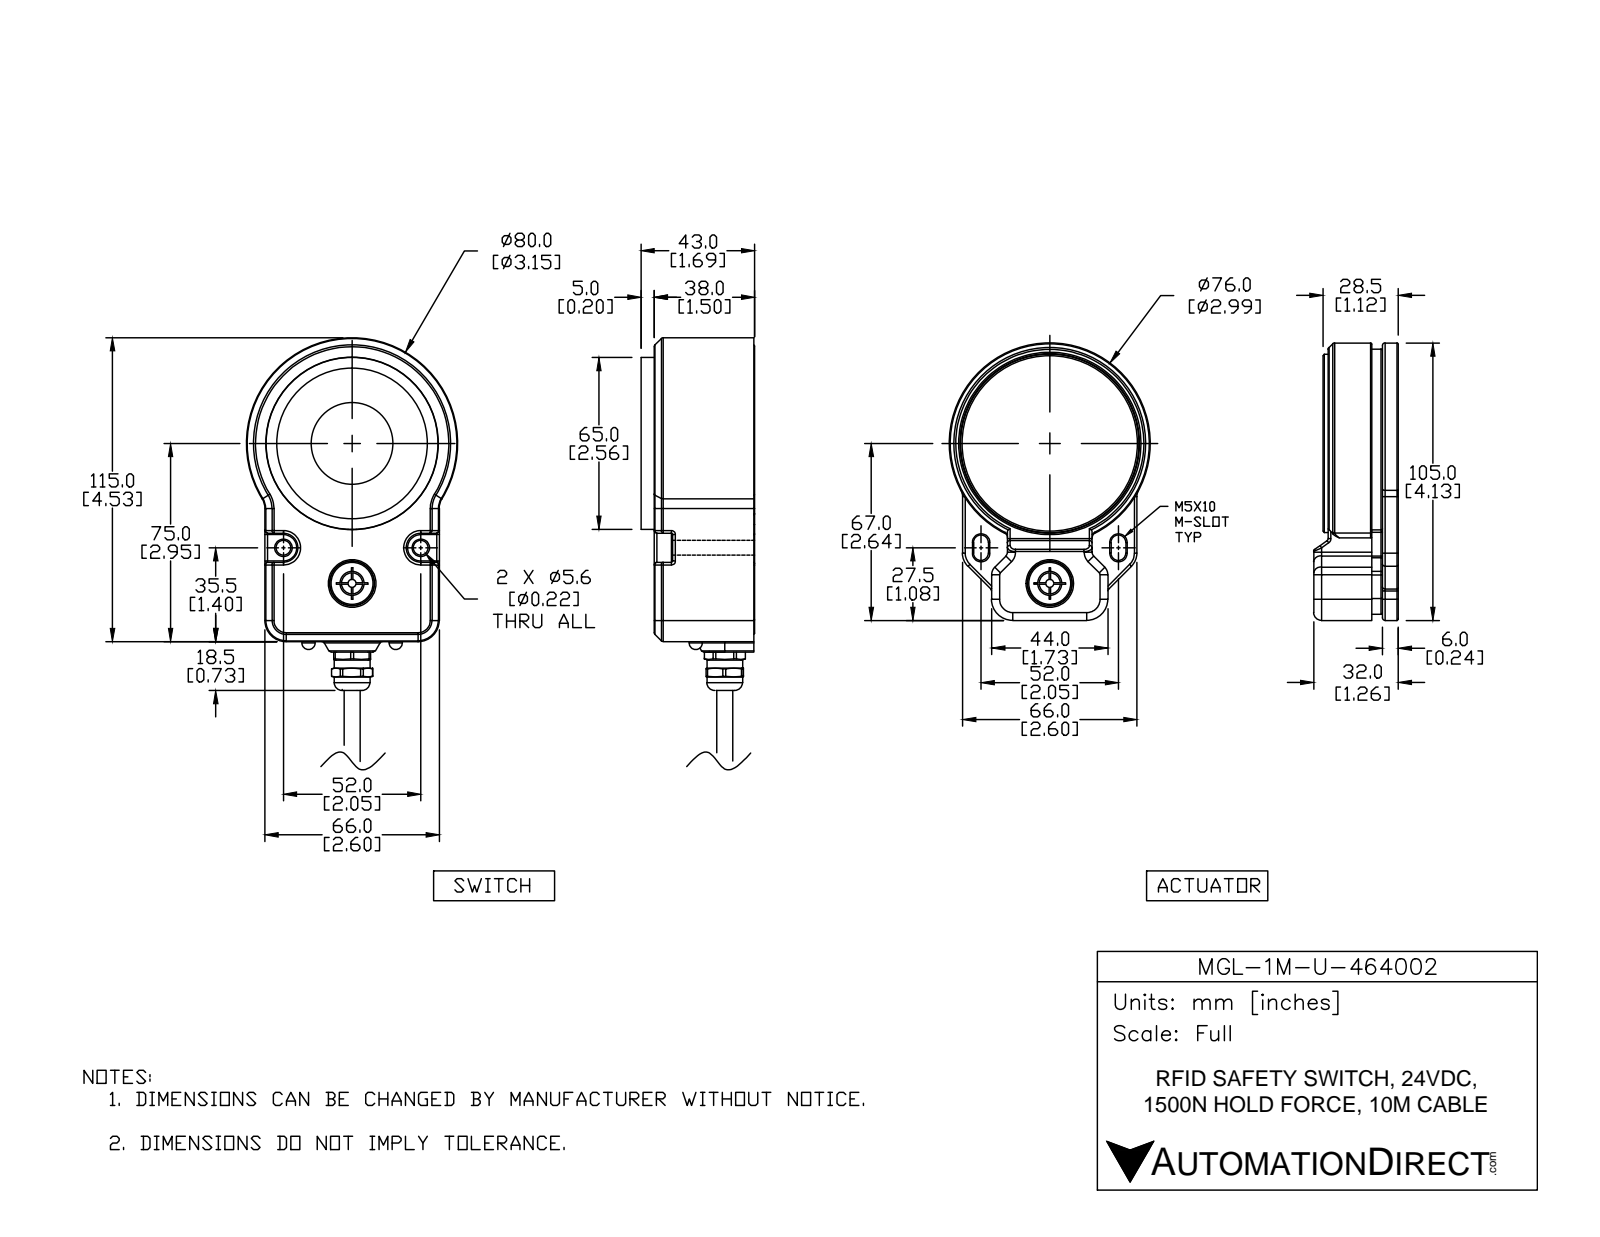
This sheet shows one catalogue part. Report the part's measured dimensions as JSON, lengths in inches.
{"part_name": "MGL-1M-U-464002; MGL-1M-U-464002_2; MGL-1M-U-464002_1", "step_written_by": "SolidWorks 2017 (AUTOMOTIVE_DESIGN)", "units": "inches", "bodies": {"solids": 19, "faces": 1753, "planar": 428, "cylindrical": 743, "other": 582}, "overall_size": [8.163, 3.15, 2.85], "volume_in3": 19.31, "surface_area_in2": 219.5, "round_holes": [[0.098, 8], [0.13, 6], [0.197, 6], [0.453, 5], [0.157, 3], [0.315, 3], [0.354, 3], [0.22, 2], [0.276, 2], [0.374, 2], [0.465, 2], [0.252, 1]], "round_bosses_or_shafts": [[0.02, 4], [0.079, 3], [0.472, 2], [0.228, 2], [0.213, 2], [0.047, 2], [2.992, 1], [2.811, 1]], "partial_cylinders_radius": [[0.02, 186], [0.039, 86], [0.079, 26], [0.012, 17], [0.118, 13], [0.157, 9], [0.217, 8], [0.024, 7]], "face_to_face_distances": [0.315, 0.236, 2.299, 1.378, 0.118, 2.614, 0.413, 2.201, 2.85, 0.65], "hole_center_spacings": [1.392, 1.969, 0.984, 1.28, 1.537, 0.787, 1.364, 0.349]}
